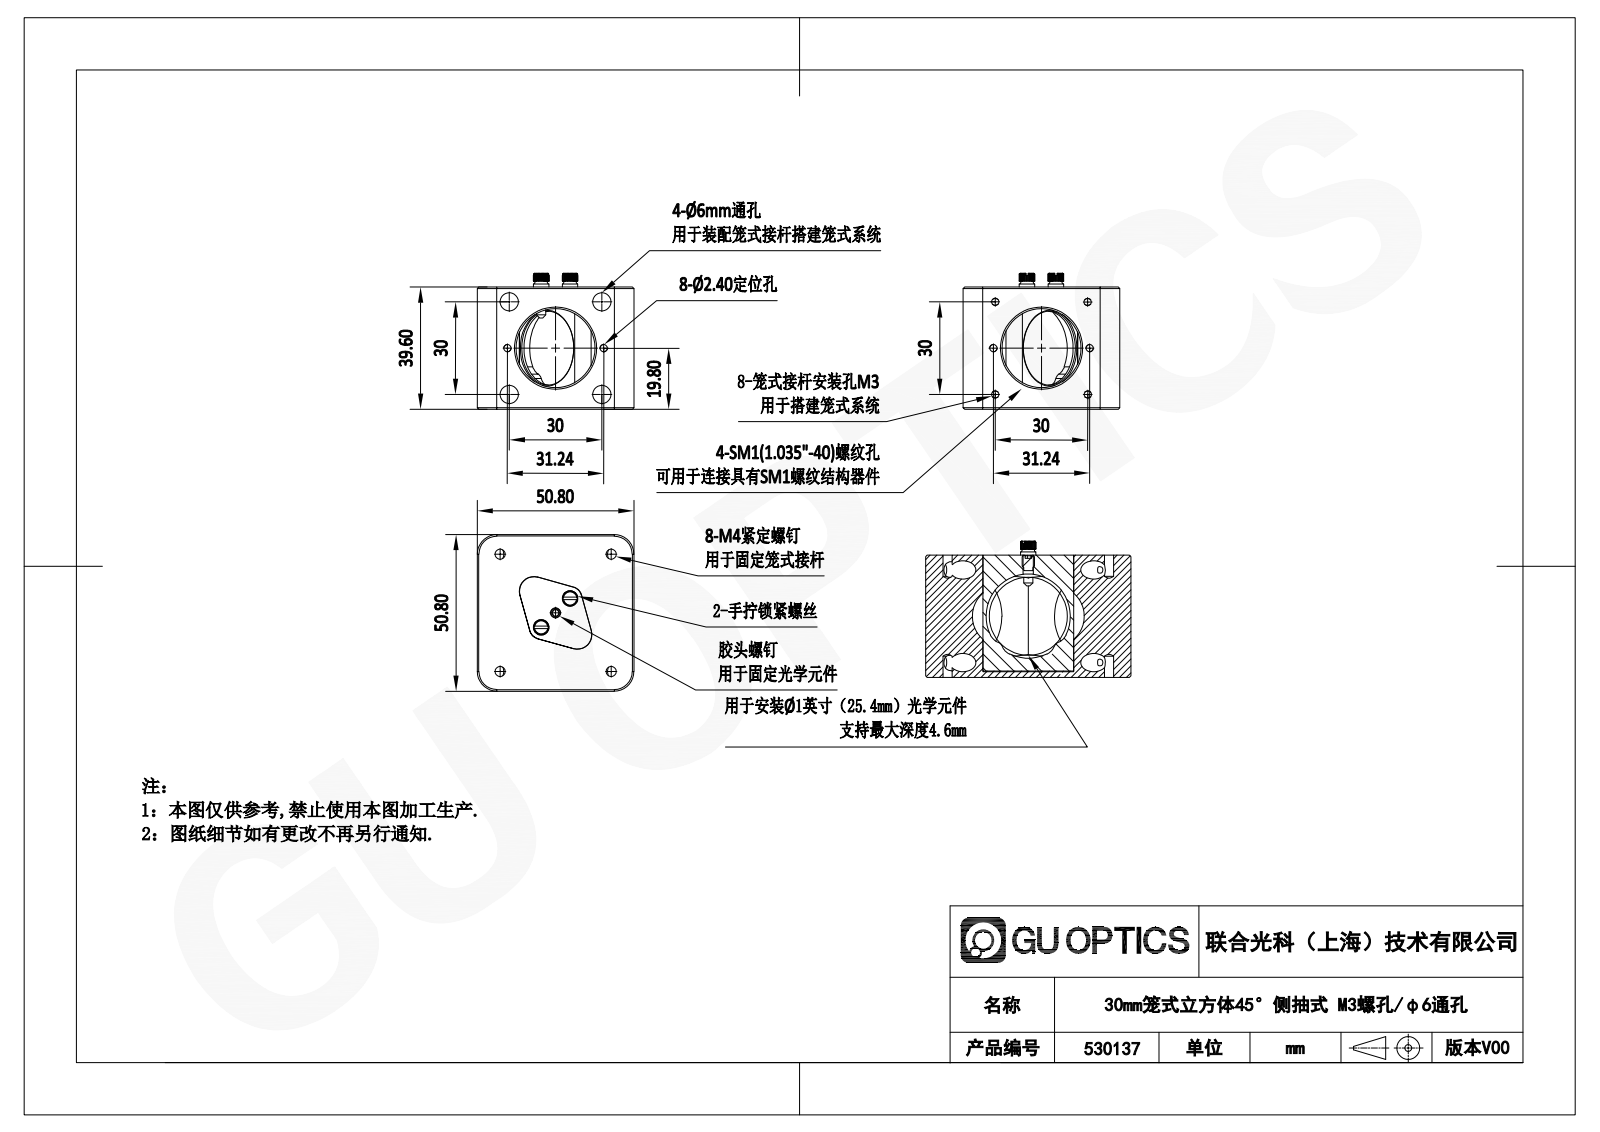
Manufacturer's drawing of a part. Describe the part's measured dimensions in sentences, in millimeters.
The part is named "530137". Its 3-D file was written by "SolidWorks 2020 (CONFIG_CONTROL_DESIGN)". It is 5 solids with 395 faces: 199 planar, 136 cylindrical and 60 other. Overall it measures 50.8 by 50.8 by 44.1 millimeters. Its volume is 53 131 cubic millimeters and its surface area 24 224 square millimeters. Round holes: 6 of diameter 2.5, 5 of diameter 3.3, 4 of diameter 2.44, 4 of diameter 6, 2 of diameter 25.69, 1 of diameter 24. Round bosses or shafts: 3 of diameter 3, 2 of diameter 5, 2 of diameter 2, 1 of diameter 4. Partial cylindrical surfaces (rounded edges, fillets, slot ends): 4 of radius 5, 4 of radius 6.35, 2 of radius 2.5, 2 of radius 3.9, 2 of radius 4, 2 of radius 4.7, 1 of radius 13.7. The main face-to-face distances are 39.6, 50.8, 3, 36.6, 2, 6, 1.8, 34.8, 0.8, 34.6. The hole center spacings are 15.01, 21.21, 30, 34.1, 15.62, 26.17, 42.43, 6.62.
